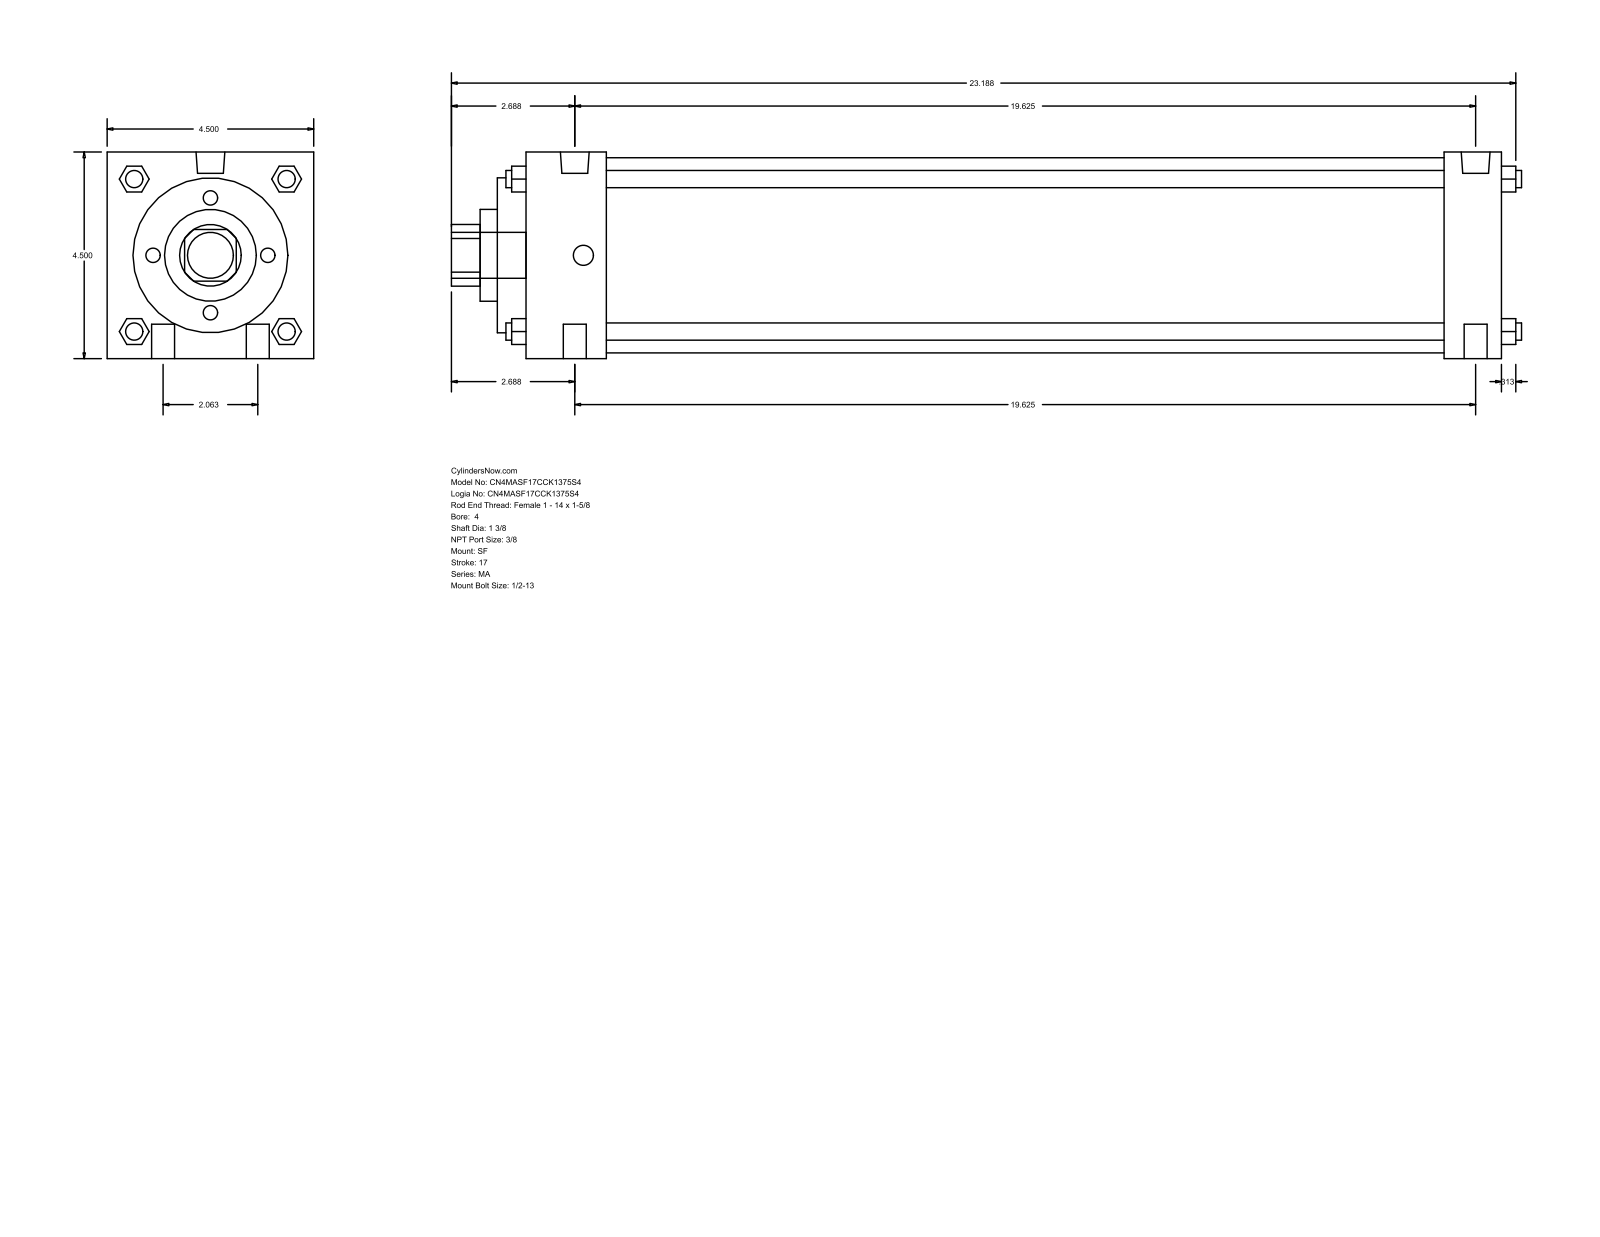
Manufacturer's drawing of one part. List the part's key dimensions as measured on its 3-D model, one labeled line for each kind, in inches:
Part name (STEP PRODUCT): MA_SF__0400_1.375
STEP written by: GSSL Pune (CONFIG_CONTROL_DESIGN)
Units: inches
Bodies: 0 solids, 126 faces (95 planar, 31 cylindrical, 0 other)
Overall size (bounding box): 23.313 × 4.5 × 4.5
Round holes (diameter × count): ⌀1.375 ×1, ⌀2 ×1, ⌀3.375 ×1, ⌀4.25 ×1
Round bosses / shafts (diameter × count): ⌀0.5 ×4, ⌀0.375 ×4, ⌀0.627 ×2, ⌀0.437 ×2, ⌀1 ×1
Partial cylindrical surfaces — rounded edges, fillets, slot ends (radius × count): R0.672 ×1
Main face-to-face distances: 4.5, 21.25, 21.875, 0.625, 20.625, 20, 1.25, 2.375, 1.75, 18.25
